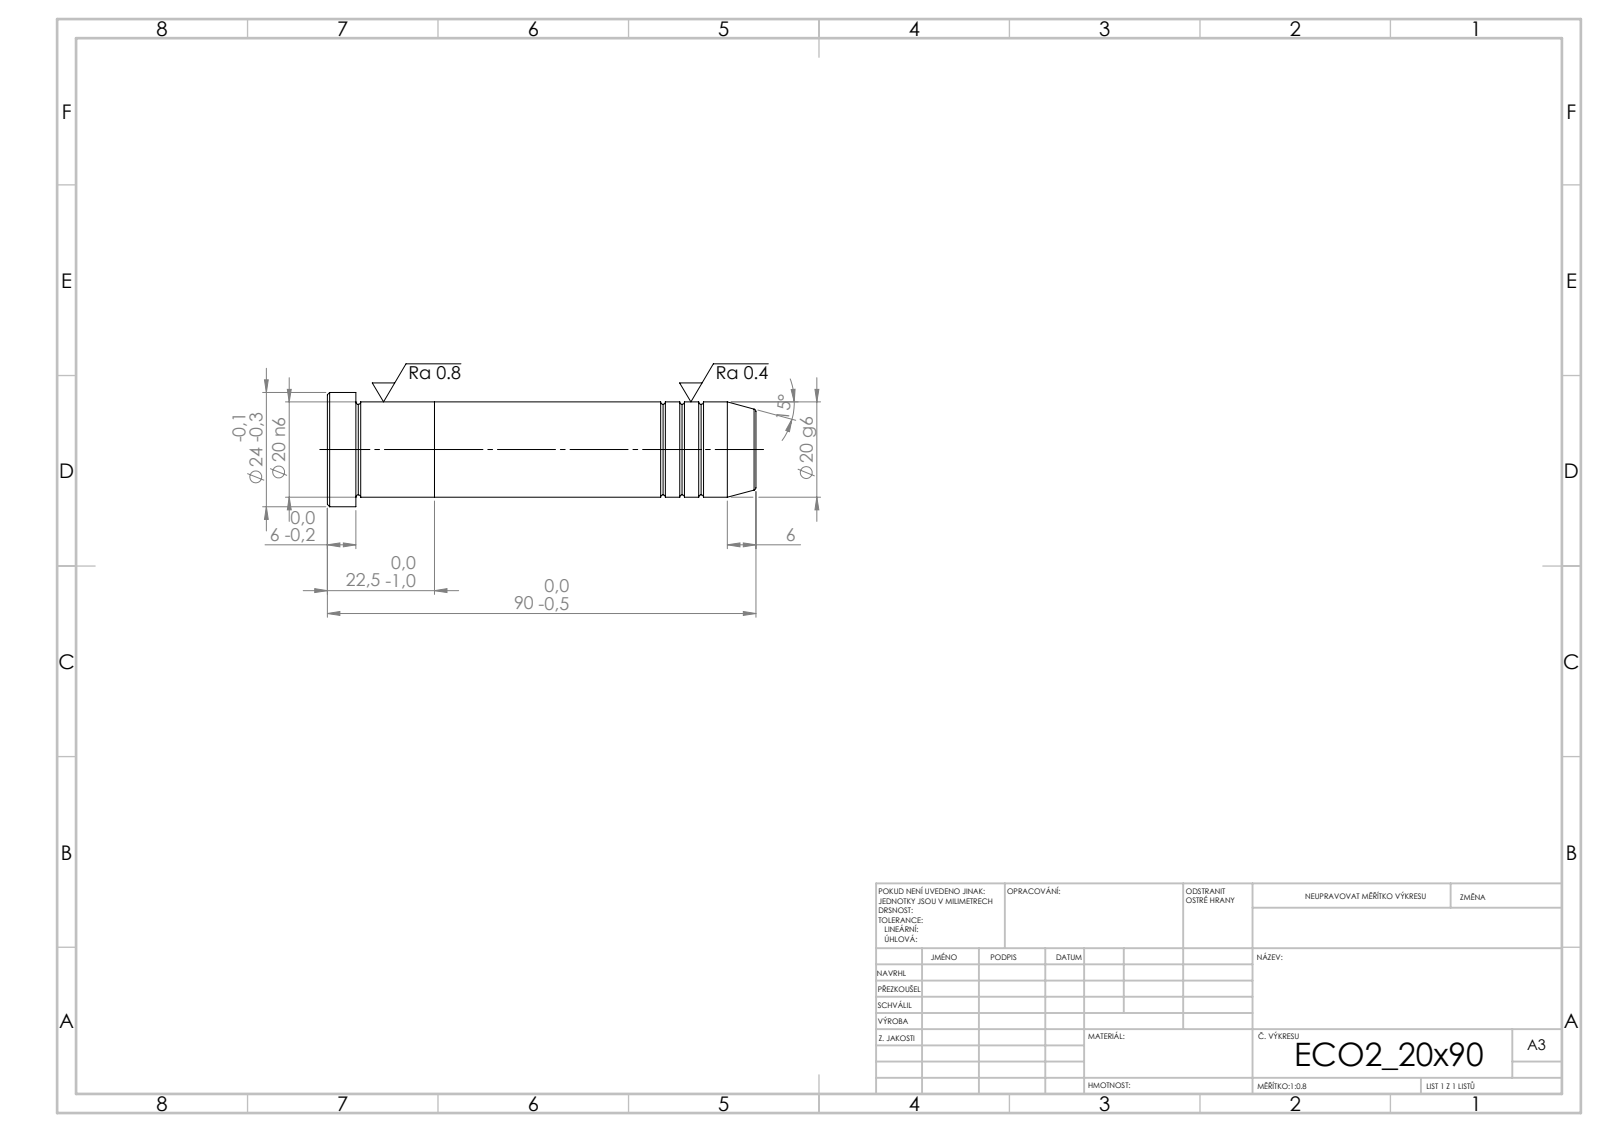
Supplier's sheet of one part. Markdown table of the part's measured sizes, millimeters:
| quantity | value |
| --- | --- |
| STEP written by | SolidWorks 2019 (CONFIG_CONTROL_DESIGN) |
| units | millimeters |
| bodies | 2 solids, 39 faces (5 planar, 12 cylindrical, 22 other) |
| overall size | 90 × 24 × 24 |
| volume | 28 710 mm³ |
| surface area | 7 255 mm² |
| round bosses / shafts (diameter × count) | 24 × 1, 20 × 1 |
| main face-to-face distances | 22.5, 67.5, 90, 84, 16.5, 6 |
